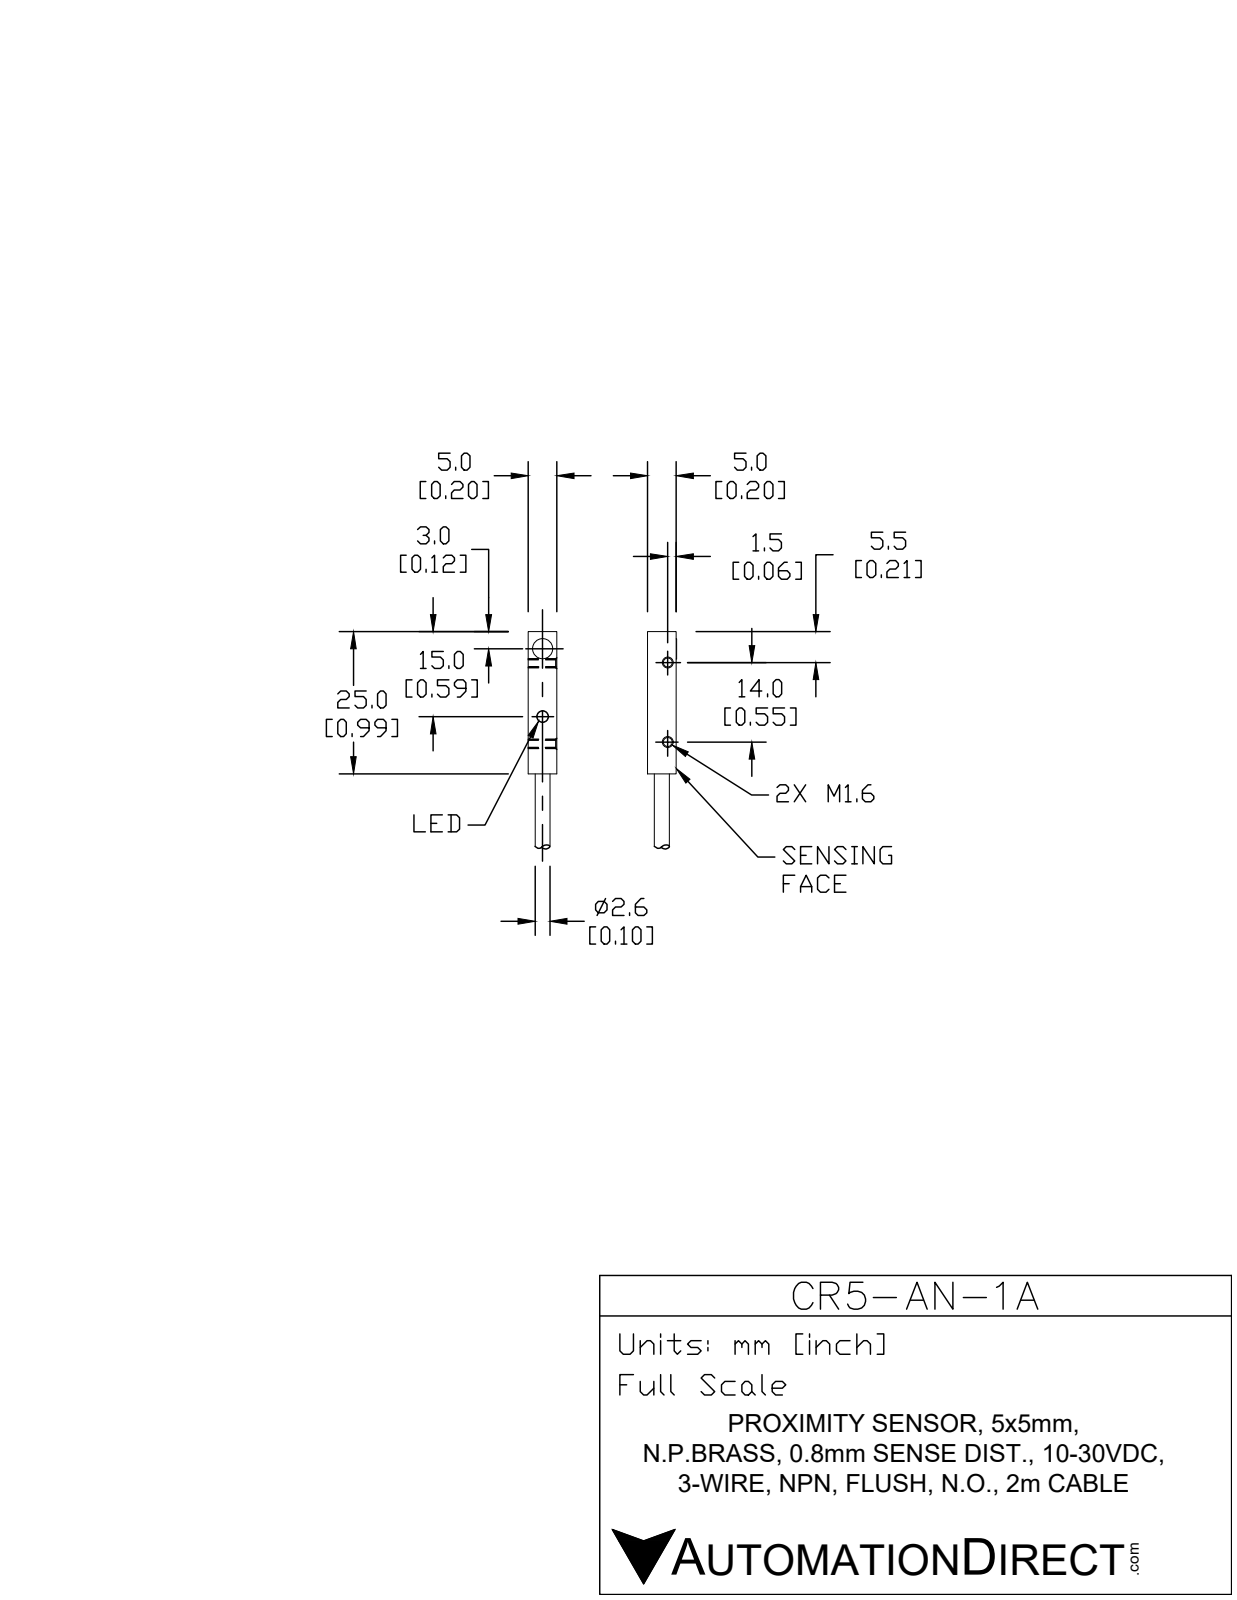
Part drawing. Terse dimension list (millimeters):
name: CR5-AN-1A
written by: SolidWorks 2017 (AUTOMOTIVE_DESIGN)
unit: mm
bodies: 1 solid, 18 faces (8 planar, 5 cylindrical, 5 other)
size: 45 × 5 × 5
volume: 720 mm³; area: 750 mm²
holes: 2× ⌀1.2, 1× ⌀1, 1× ⌀2.6
bosses: 1× ⌀2.6
face distances: 5, 25, 4.7, 20, 45
hole spacings: 12, 14
